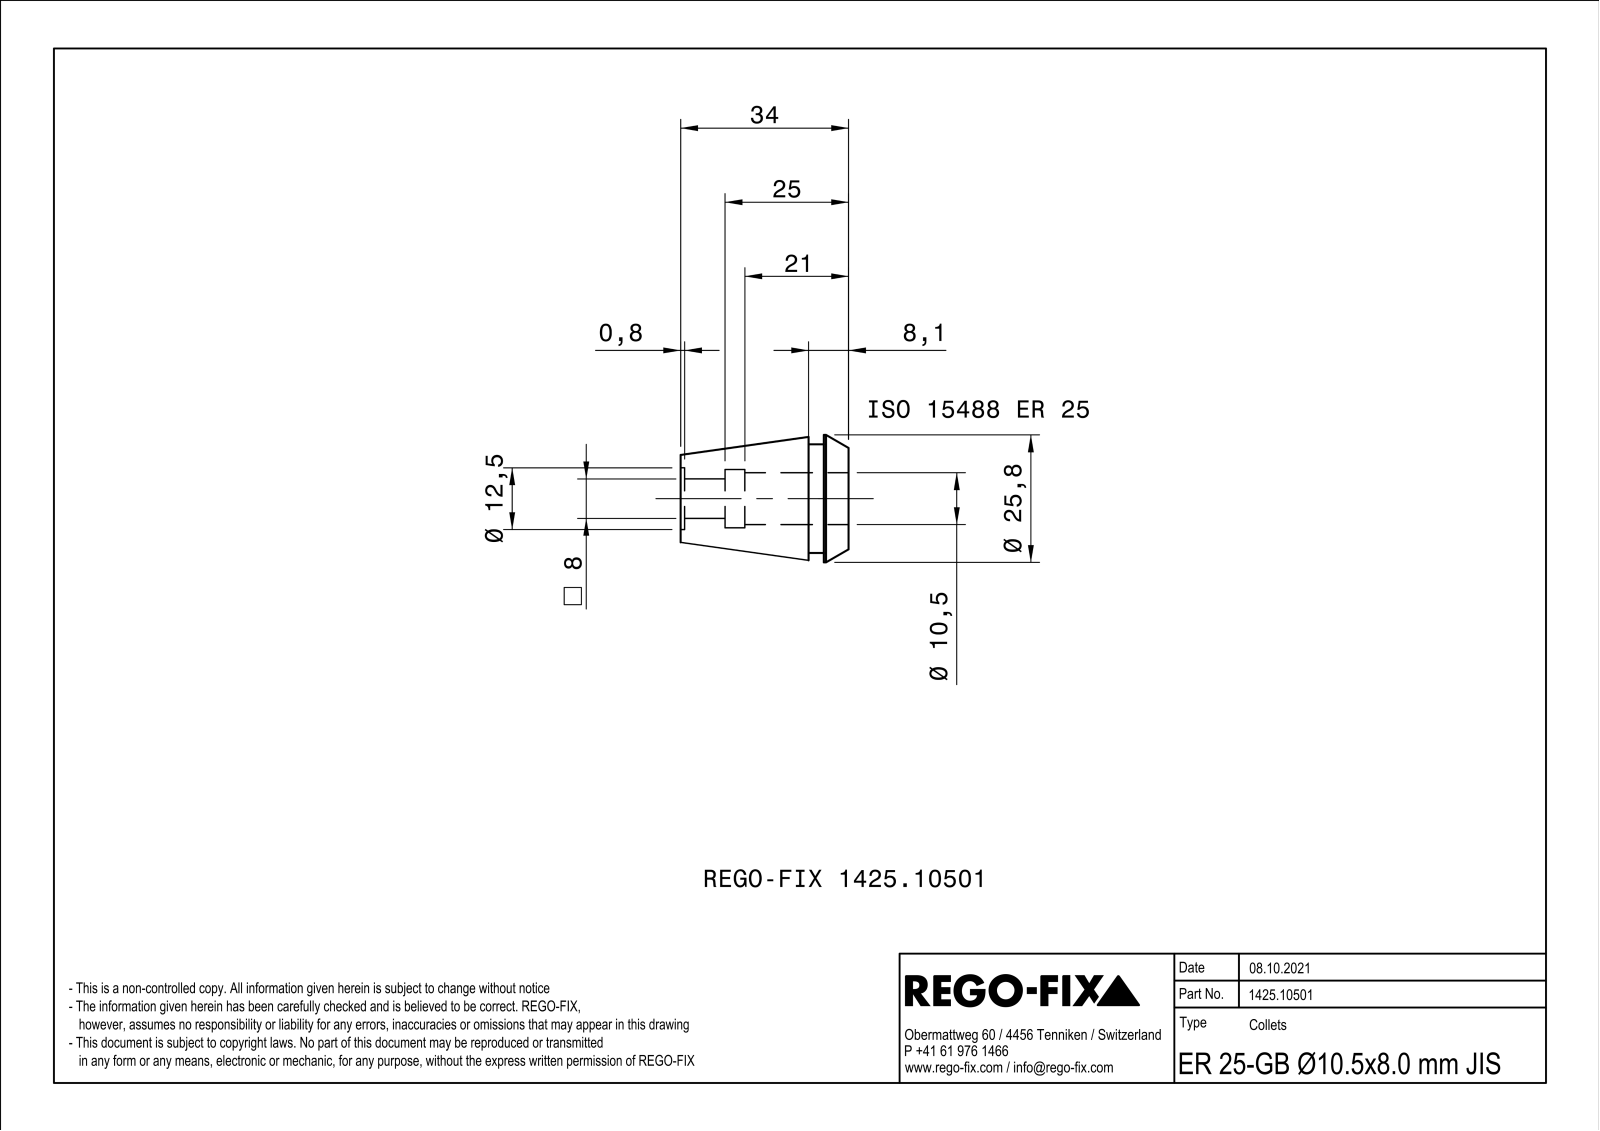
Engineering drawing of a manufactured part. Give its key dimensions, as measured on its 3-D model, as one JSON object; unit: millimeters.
{"part_name": "NOCUT", "step_written_by": "SIEMENS PLM Software Solid Edge ST10 (AUTOMOTIVE_DESIGN)", "units": "millimeters", "bodies": {"solids": 1, "faces": 132, "planar": 60, "cylindrical": 28, "other": 44}, "overall_size": [34, 25.79, 25.79], "volume_mm3": 8488, "surface_area_mm2": 6378, "round_holes": [[10.5, 1], [11.8, 1]], "round_bosses_or_shafts": [[25.8, 1], [22, 1]], "partial_cylinders_radius": [[4.7, 1]], "face_to_face_distances": [0.8, 5, 8.1, 3.1, 3.85, 4.65, 8.5, 20.8, 15.8, 12.7]}
